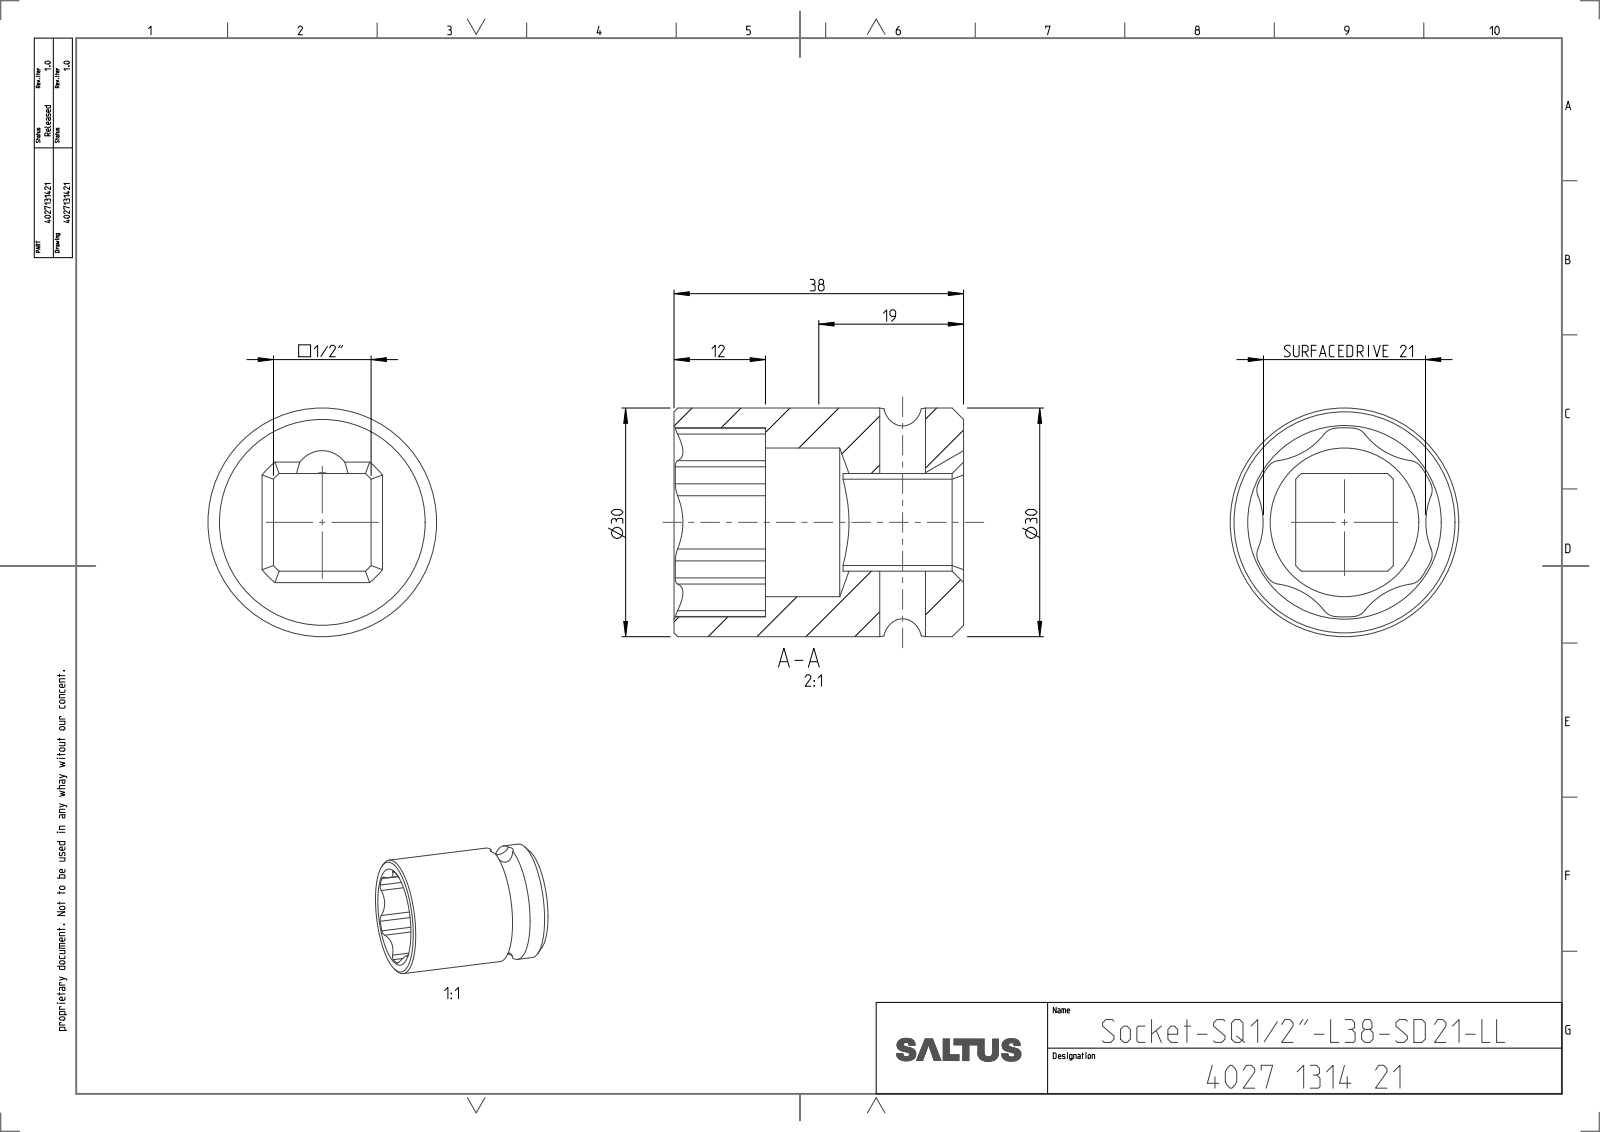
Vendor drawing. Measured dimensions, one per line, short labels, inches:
name: 4027131421
written by: CREO PARAMETRIC BY PTC INC, 2022414 (CONFIG_CONTROL_DESIGN)
unit: in
bodies: 1 solid, 65 faces (12 planar, 39 cylindrical, 14 other)
size: 1.496 × 1.181 × 1.181
volume: 0.907 in³; area: 10.94 in²
holes: 1× ⌀0.236, 1× ⌀0.768
bosses: 1× ⌀1.181
rounds: 12× R0.079, 6× R0.366, 1× R0.157, 1× R0.337, 1× R0.489
face distances: 0.505, 1.496, 1.024, 0.472
